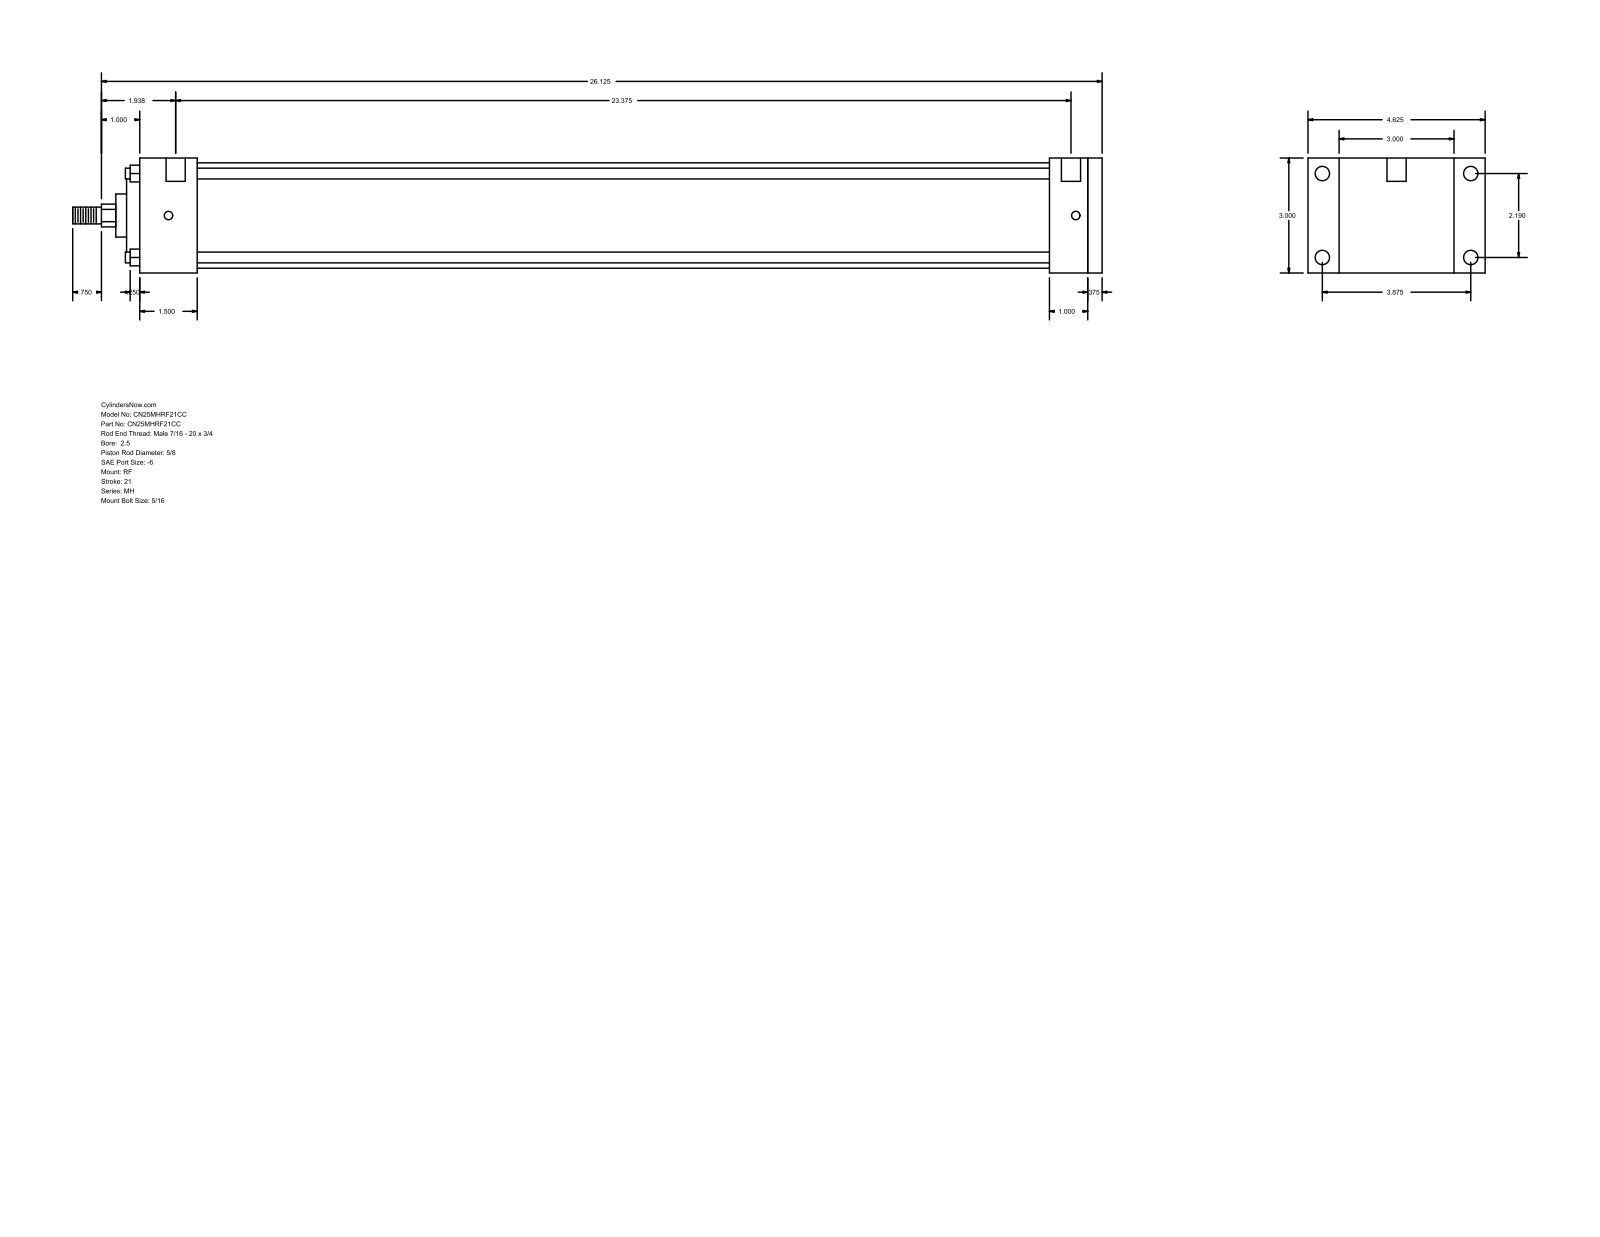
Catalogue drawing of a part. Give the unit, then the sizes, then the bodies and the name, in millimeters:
Units: millimetres
Overall size (bounding box): 682.62 × 117.47 × 76.2
Round holes (diameter × count): ⌀5.56 ×4, ⌀9.53 ×4, ⌀12.7 ×2
Round bosses / shafts (diameter × count): ⌀7.14 ×4, ⌀69.85 ×1, ⌀55.55 ×1, ⌀28.57 ×1, ⌀15.88 ×1, ⌀11.11 ×1
Partial cylindrical surfaces — rounded edges, fillets, slot ends (radius × count): R7.54 ×1
Main face-to-face distances: 76.2, 9.53, 638.18, 628.65, 25.4, 34.93, 38.1, 603.25, 565.15, 590.55
Hole centre spacings: 55.62, 98.42, 113.05, 601.66, 3.17, 4.76, 593.73, 596.9
Bodies: 0 solids, 94 faces (65 planar, 29 cylindrical, 0 other)
Part name (STEP PRODUCT): MH_RF__0250_0.625
STEP written by: GSSL Pune (CONFIG_CONTROL_DESIGN)
